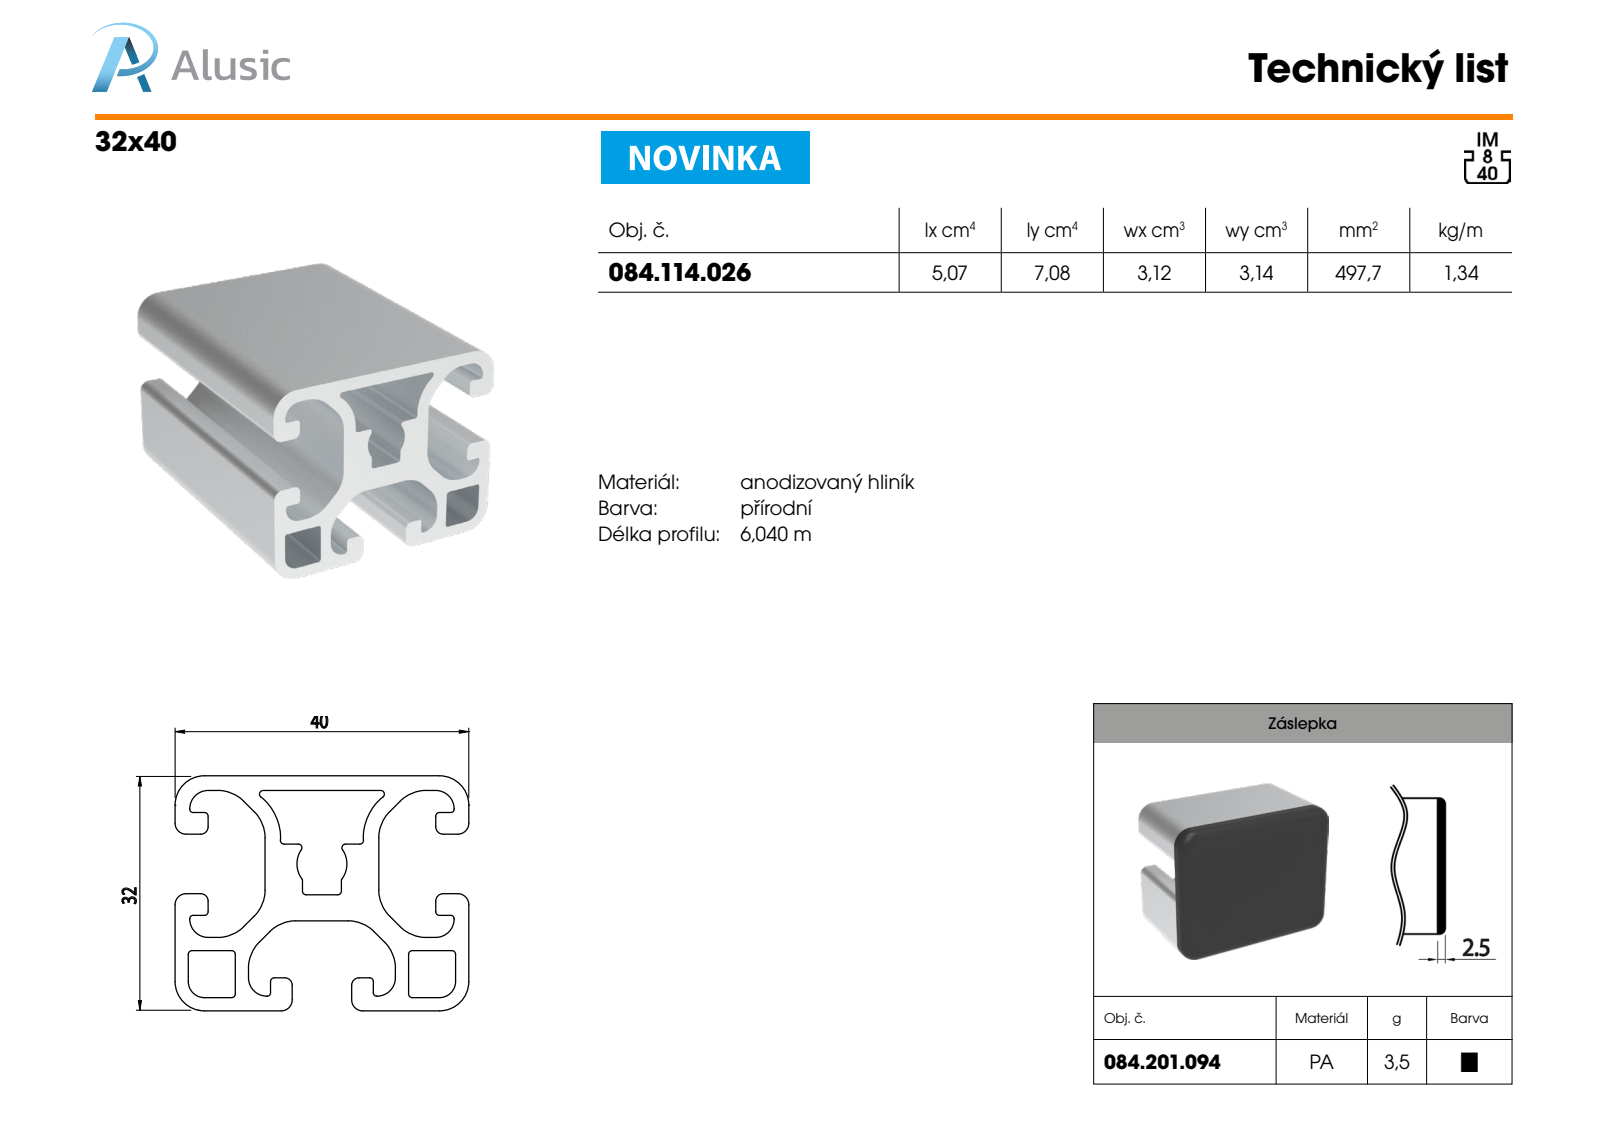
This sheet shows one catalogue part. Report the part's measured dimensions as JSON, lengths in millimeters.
{"part_name": "084.114.26", "step_written_by": "SolidWorks 2018 (AUTOMOTIVE_DESIGN)", "units": "millimeters", "bodies": {"solids": 1, "faces": 130, "planar": 62, "cylindrical": 68, "other": 0}, "overall_size": [100, 40, 32], "volume_mm3": 49768, "surface_area_mm2": 39395, "partial_cylinders_radius": [[0.5, 22], [5, 12], [0.45, 6], [1, 6], [1.5, 6], [2.5, 6], [4, 4], [2.2, 2]], "face_to_face_distances": [30, 8.2, 12.25, 32, 1.8, 2, 10.45, 4.05, 19.55, 3.7]}
